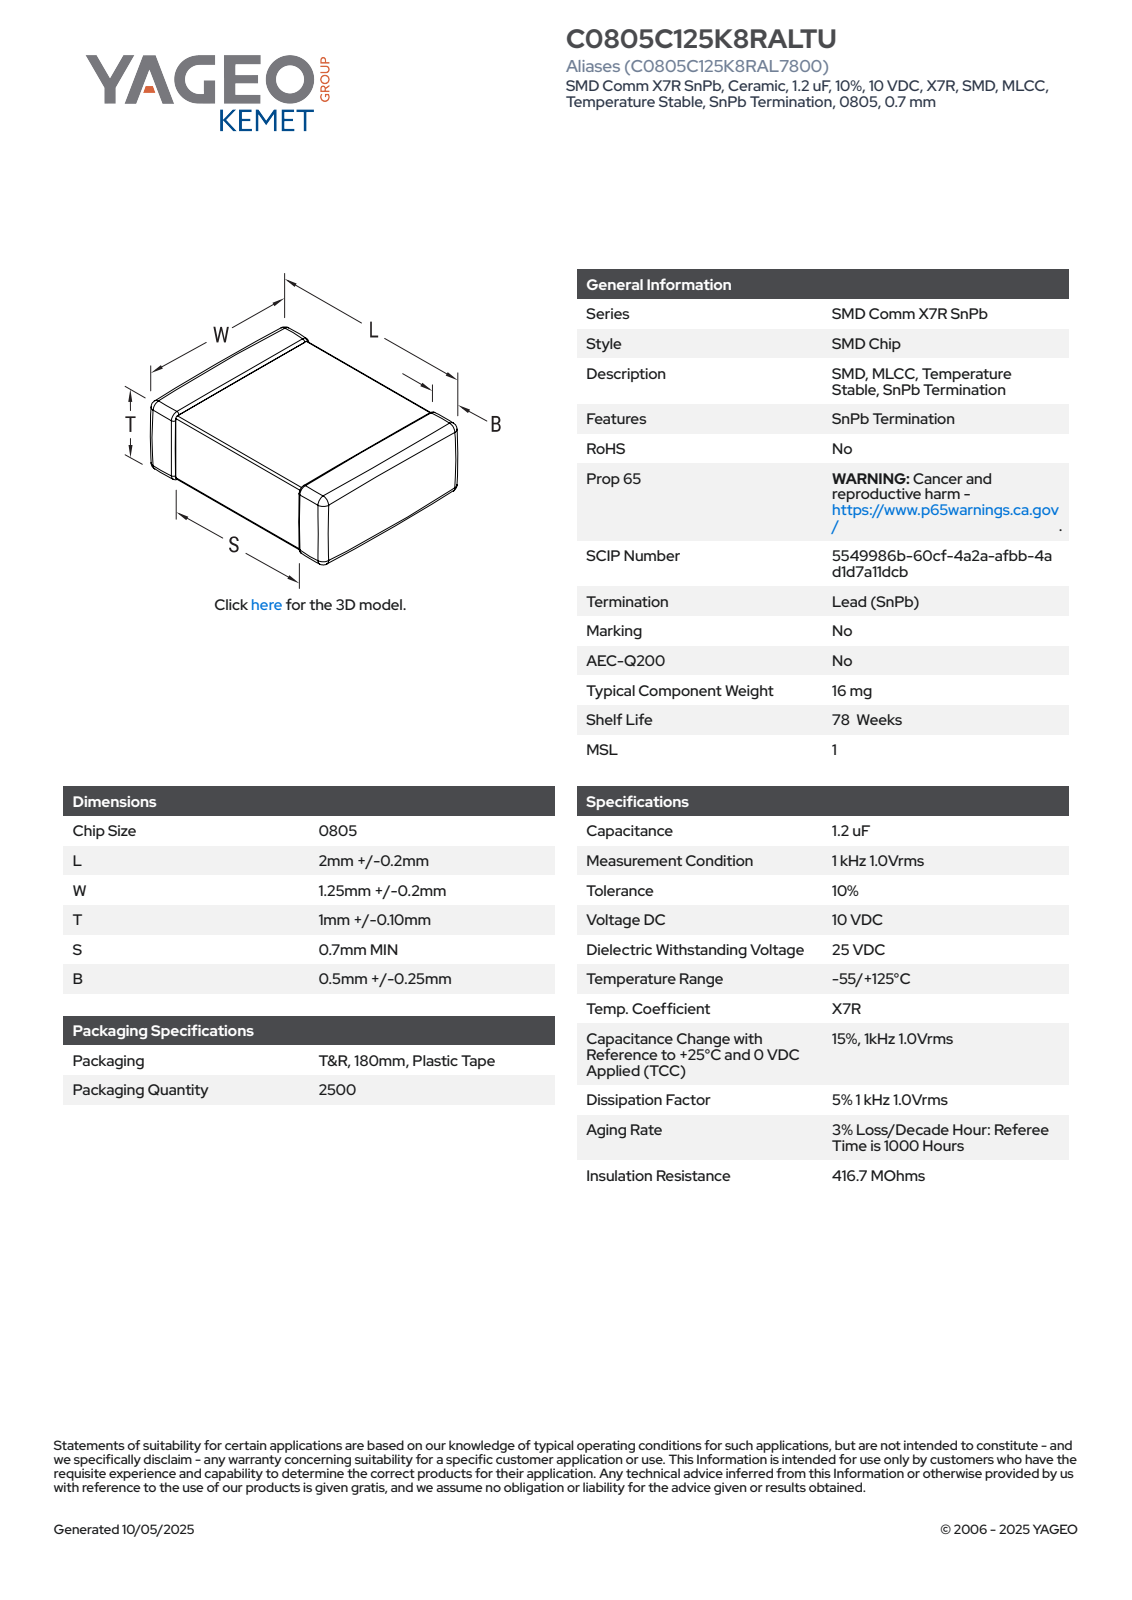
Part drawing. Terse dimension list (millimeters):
name: CCS_CCSTD_0805_L2.2W1.45T1.1B0.5
written by: SolidWorks 2021 (AUTOMOTIVE_DESIGN)
unit: mm
bodies: 4 solids, 121 faces (71 planar, 34 cylindrical, 16 other)
size: 2.2 × 1.45 × 1.1
volume: 3 mm³; area: 14 mm²
face distances: 1.07, 1.1, 2.2, 1.45, 1.42, 1.04, 1.39, 0.97, 1.23, 1.19
